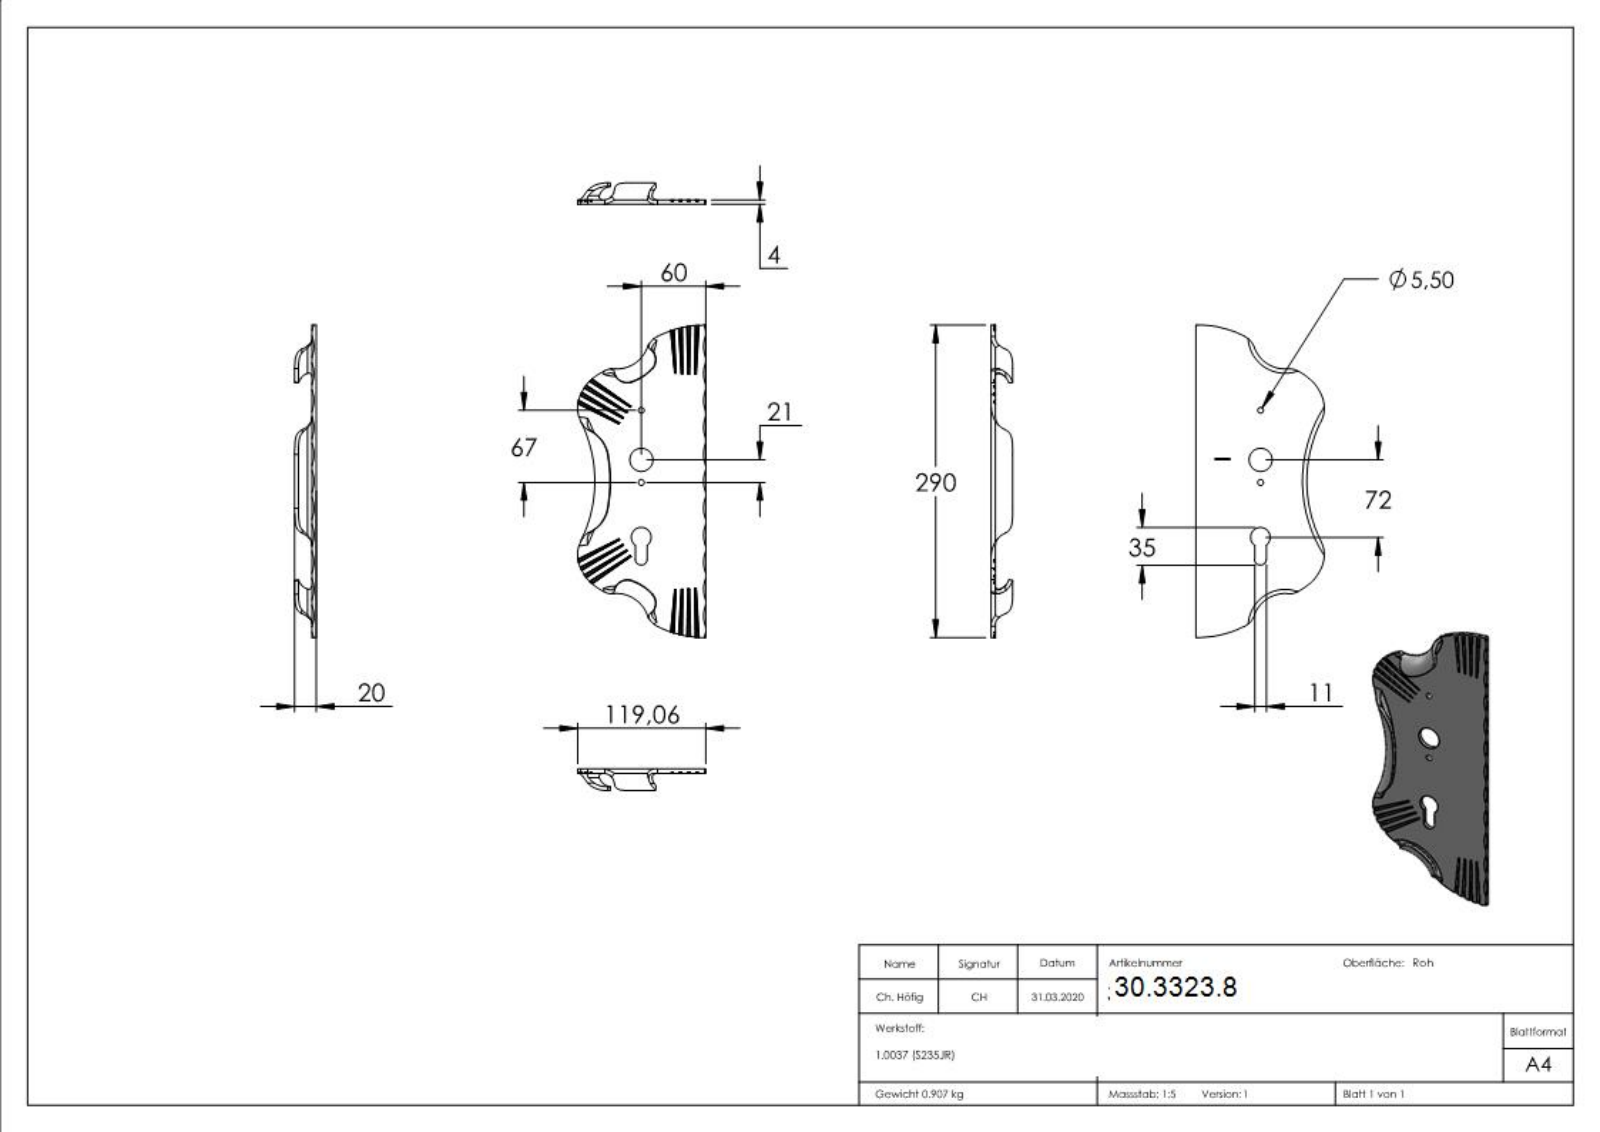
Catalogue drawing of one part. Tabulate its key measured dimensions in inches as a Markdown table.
| quantity | value |
| --- | --- |
| part name | 3840 |
| STEP written by | SolidWorks 2015 (CONFIG_CONTROL_DESIGN) |
| units | inches |
| bodies | 1 solid, 405 faces (160 planar, 117 cylindrical, 128 other) |
| overall size | 11.417 × 4.687 × 0.787 |
| volume | 7.098 in³ |
| surface area | 98.62 in² |
| round holes (diameter × count) | 0.217 × 2, 0.728 × 1, 0.846 × 1 |
| partial cylindrical surfaces (radius × count) | 0.012 × 96, 0.394 × 4, 0.687 × 2, 0.765 × 2, 1.142 × 2, 2.007 × 2, 2.151 × 2, 3.82 × 2 |
| main face-to-face distances | 0.157, 2.579, 0.433, 2.146, 0.154, 11.417, 0.08, 0.391, 0.117, 0.015 |
| hole center spacings | 0.827, 1.811, 2.008, 2.638, 2.835, 4.646 |
